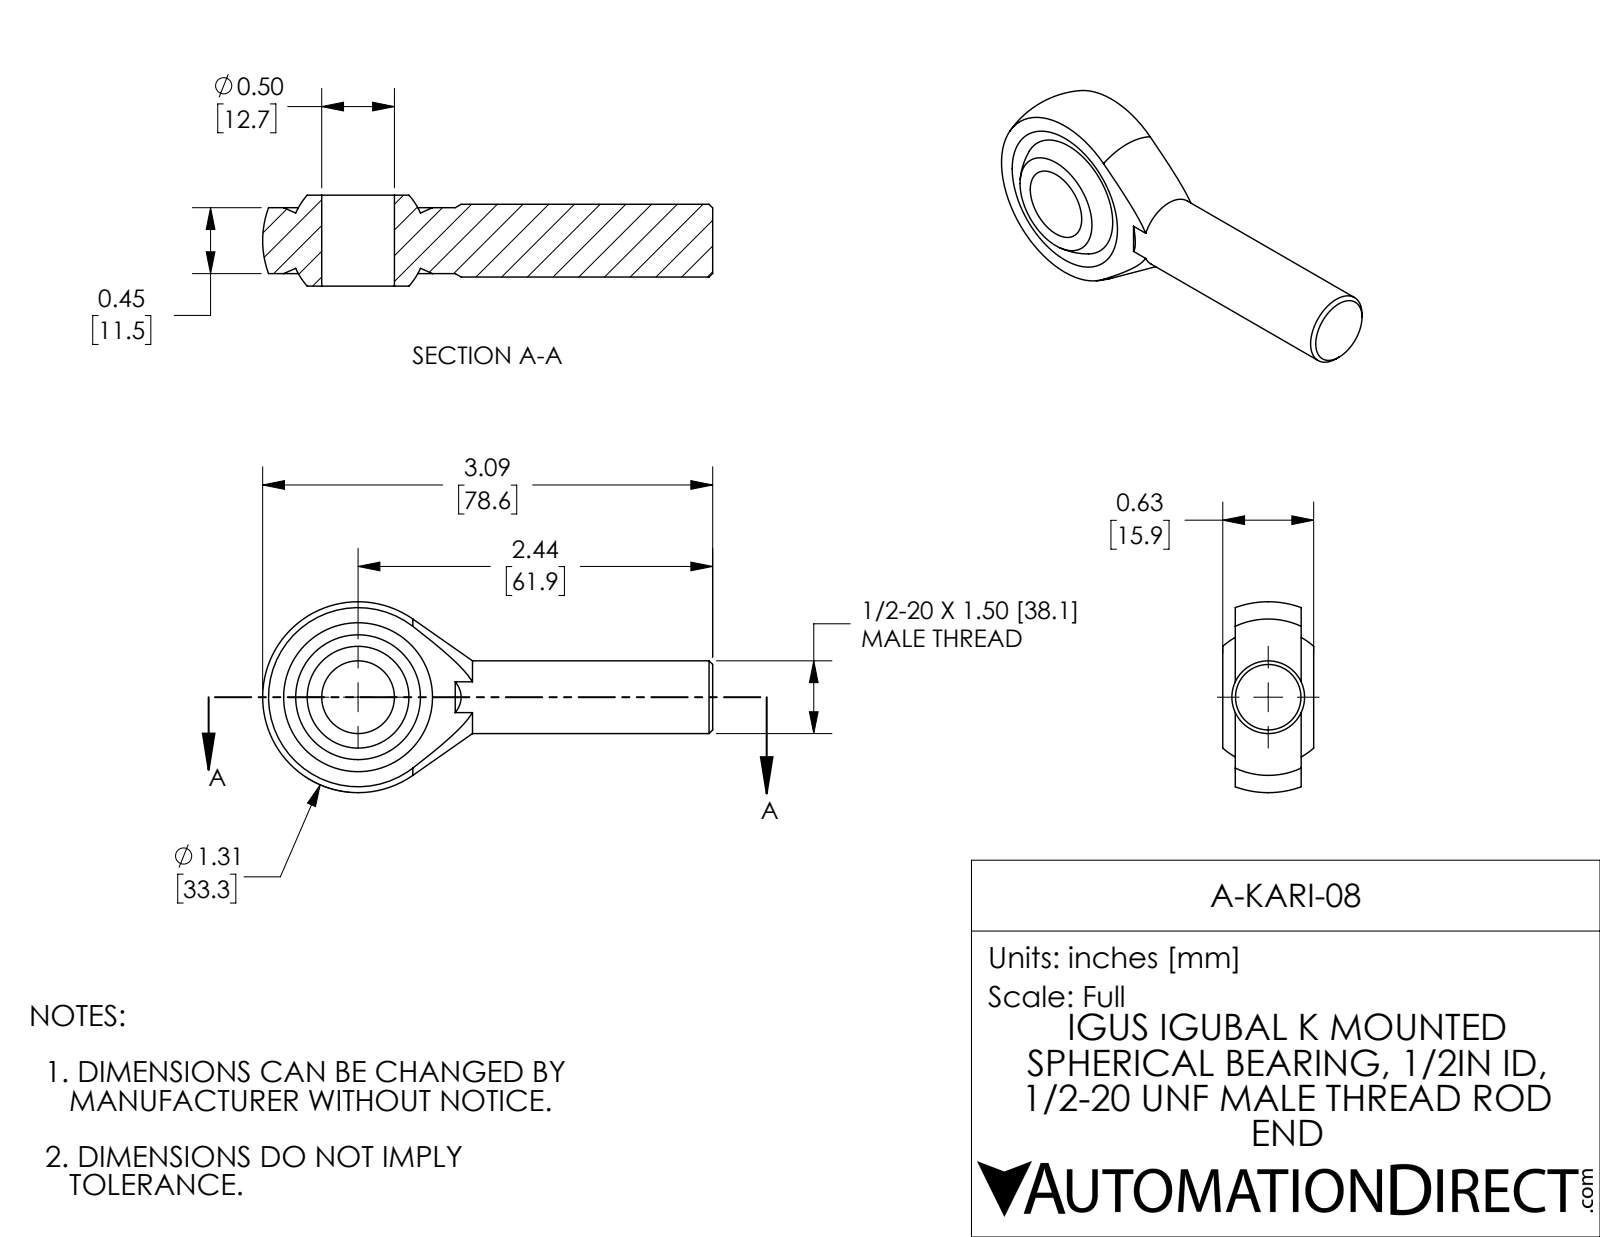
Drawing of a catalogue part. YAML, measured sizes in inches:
part_name: "A-KARI-08"
step_written_by: "SolidWorks 2017 (AUTOMOTIVE_DESIGN)"
units: inches
bodies: {solids: 1, faces: 27, planar: 7, cylindrical: 4, other: 16}
overall_size: [3.094, 1.312, 0.625]
volume: 0.908
surface_area: 8.111
round_holes:
  - {diameter: 0.5, count: 1}
round_bosses_or_shafts:
  - {diameter: 0.5, count: 1}
face_to_face_distances: [0.453, 0.086, 0.539, 0.625]
